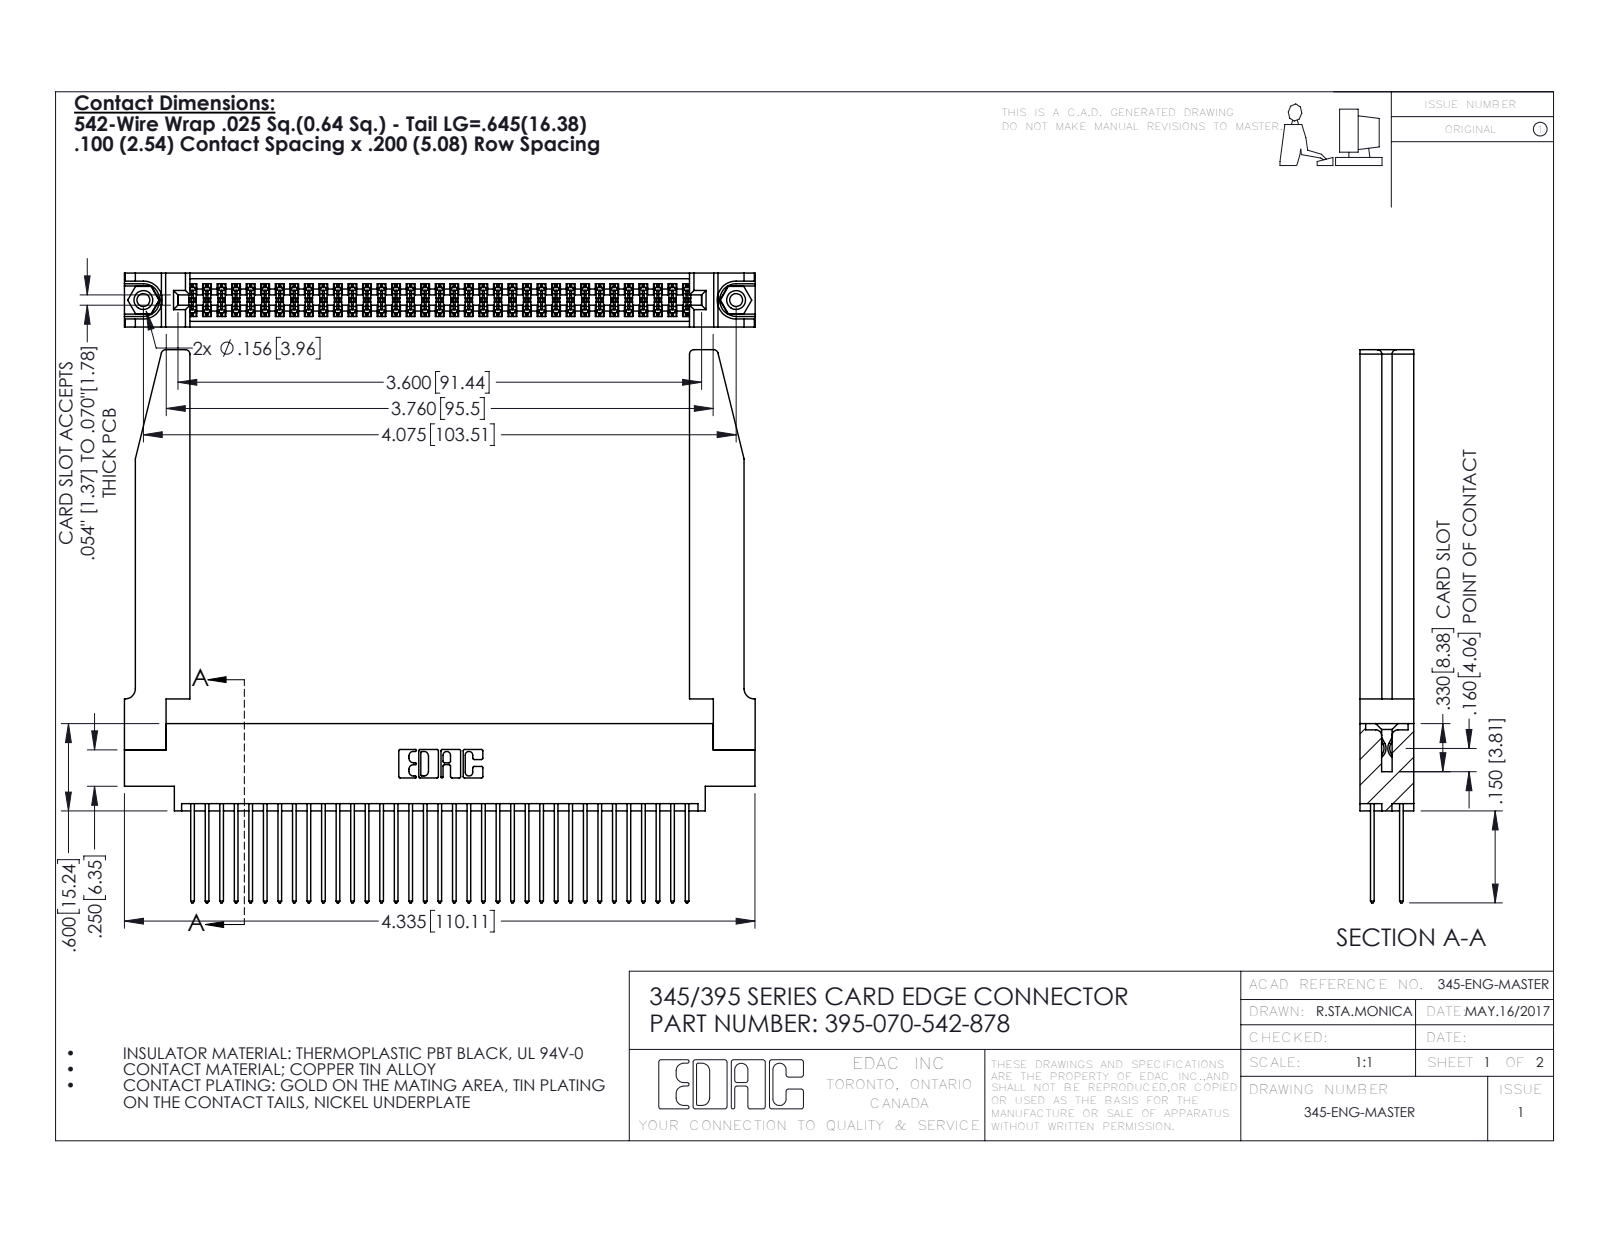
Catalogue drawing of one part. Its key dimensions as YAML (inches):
part_name: "345-292-001_345-293-142; 345-250-001_345-250-001-102; 395-070-542-878; 345-220-078_345-220-078 (+1 more)"
step_written_by: "SolidWorks 2016 (CONFIG_CONTROL_DESIGN)"
units: inches
bodies: {solids: 75, faces: 3864, planar: 2536, cylindrical: 1276, other: 52}
overall_size: [4.336, 3.802, 0.37]
volume: 1.136
surface_area: 37.83
round_holes:
  - {diameter: 0.089, count: 2}
  - {diameter: 0.125, count: 2}
  - {diameter: 0.156, count: 2}
  - {diameter: 0.064, count: 1}
round_bosses_or_shafts:
  - {diameter: 0.155, count: 2}
partial_cylinders:
  - {radius: 0.006, count: 105}
  - {radius: 0.01, count: 70}
  - {radius: 0.01, count: 22}
  - {radius: 0.03, count: 8}
  - {radius: 0.007, count: 6}
  - {radius: 0.031, count: 6}
  - {radius: 0.026, count: 3}
  - {radius: 0.014, count: 2}
face_to_face_distances: [0.072, 0.298, 0.37, 0.098, 0.272, 0.025, 0.2, 0.225, 0.175, 0.148]
hole_center_spacings: [0.27, 3.839, 4.075]
